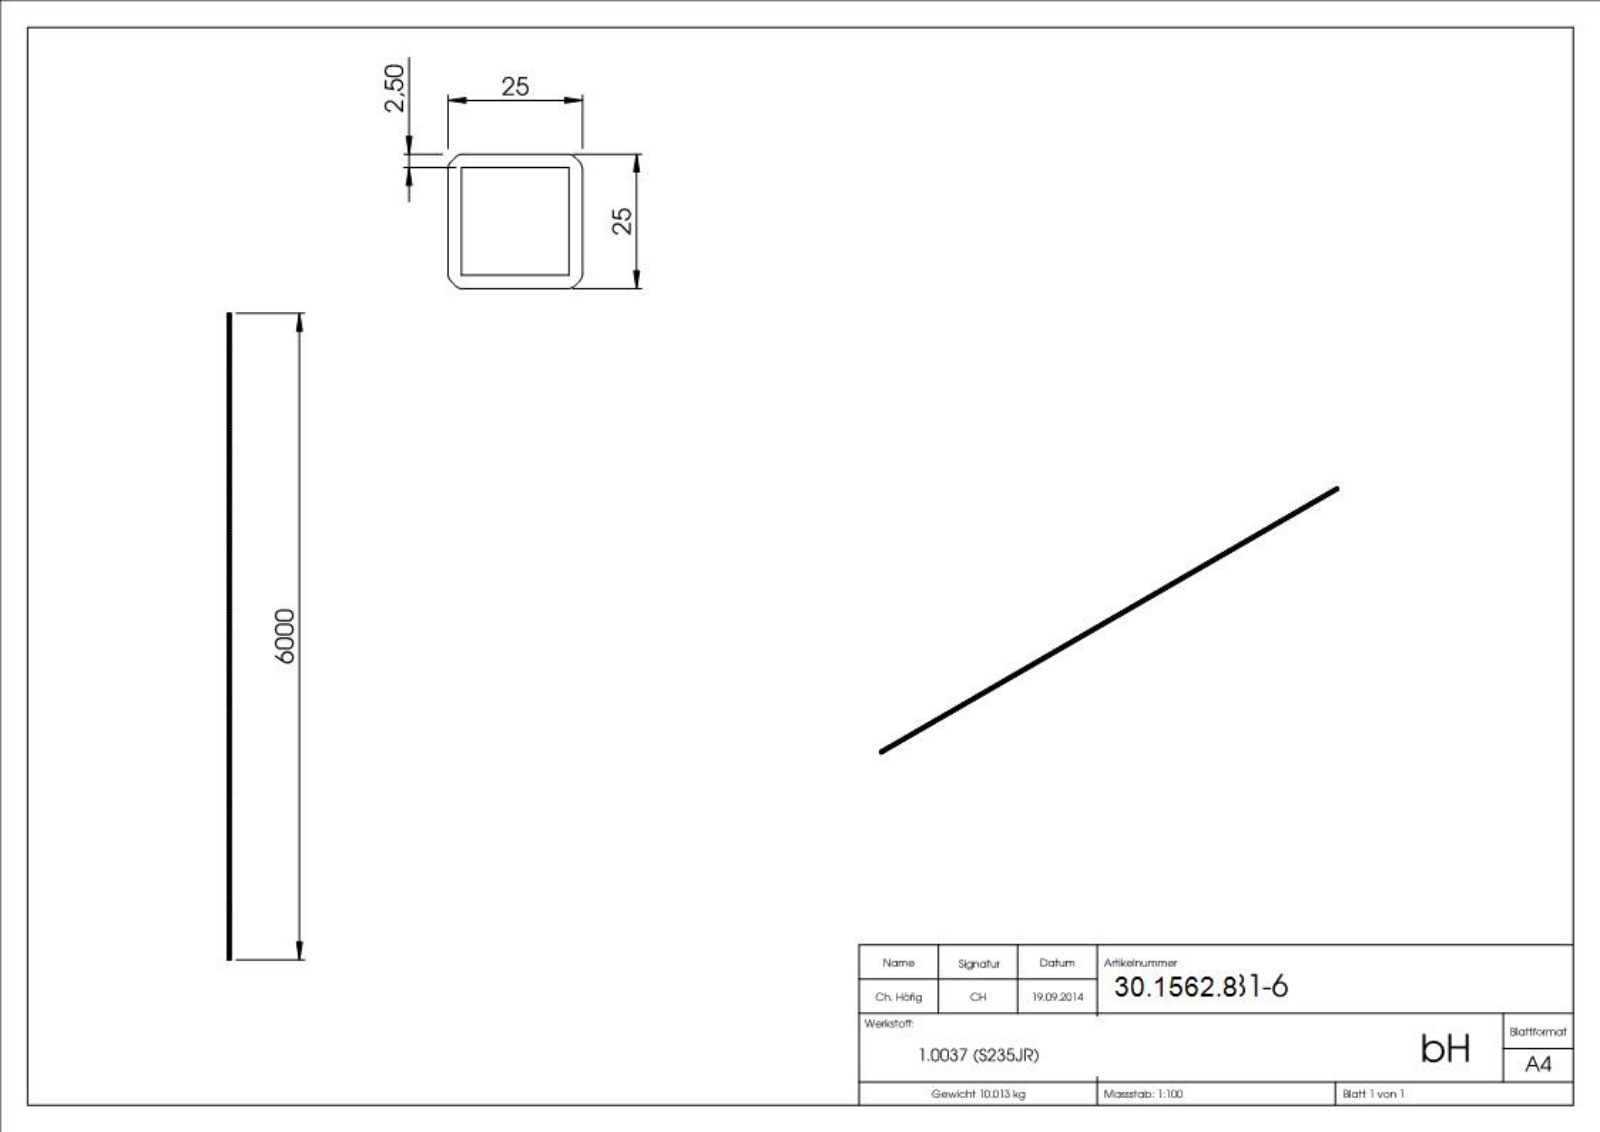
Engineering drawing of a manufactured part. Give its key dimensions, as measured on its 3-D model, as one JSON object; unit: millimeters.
{"part_name": "6981-6", "step_written_by": "SolidWorks 2018 (CONFIG_CONTROL_DESIGN)", "units": "millimeters", "bodies": {"solids": 1, "faces": 3611, "planar": 107, "cylindrical": 1108, "other": 2396}, "overall_size": [6000, 25, 25], "volume_mm3": 1276000, "surface_area_mm2": 1025000, "partial_cylinders_radius": [[1.25, 4], [3.75, 4]], "face_to_face_distances": [2.5, 22.5, 25, 20, 6000, 5500, 500, 2.4, 20.1, 22.6]}
